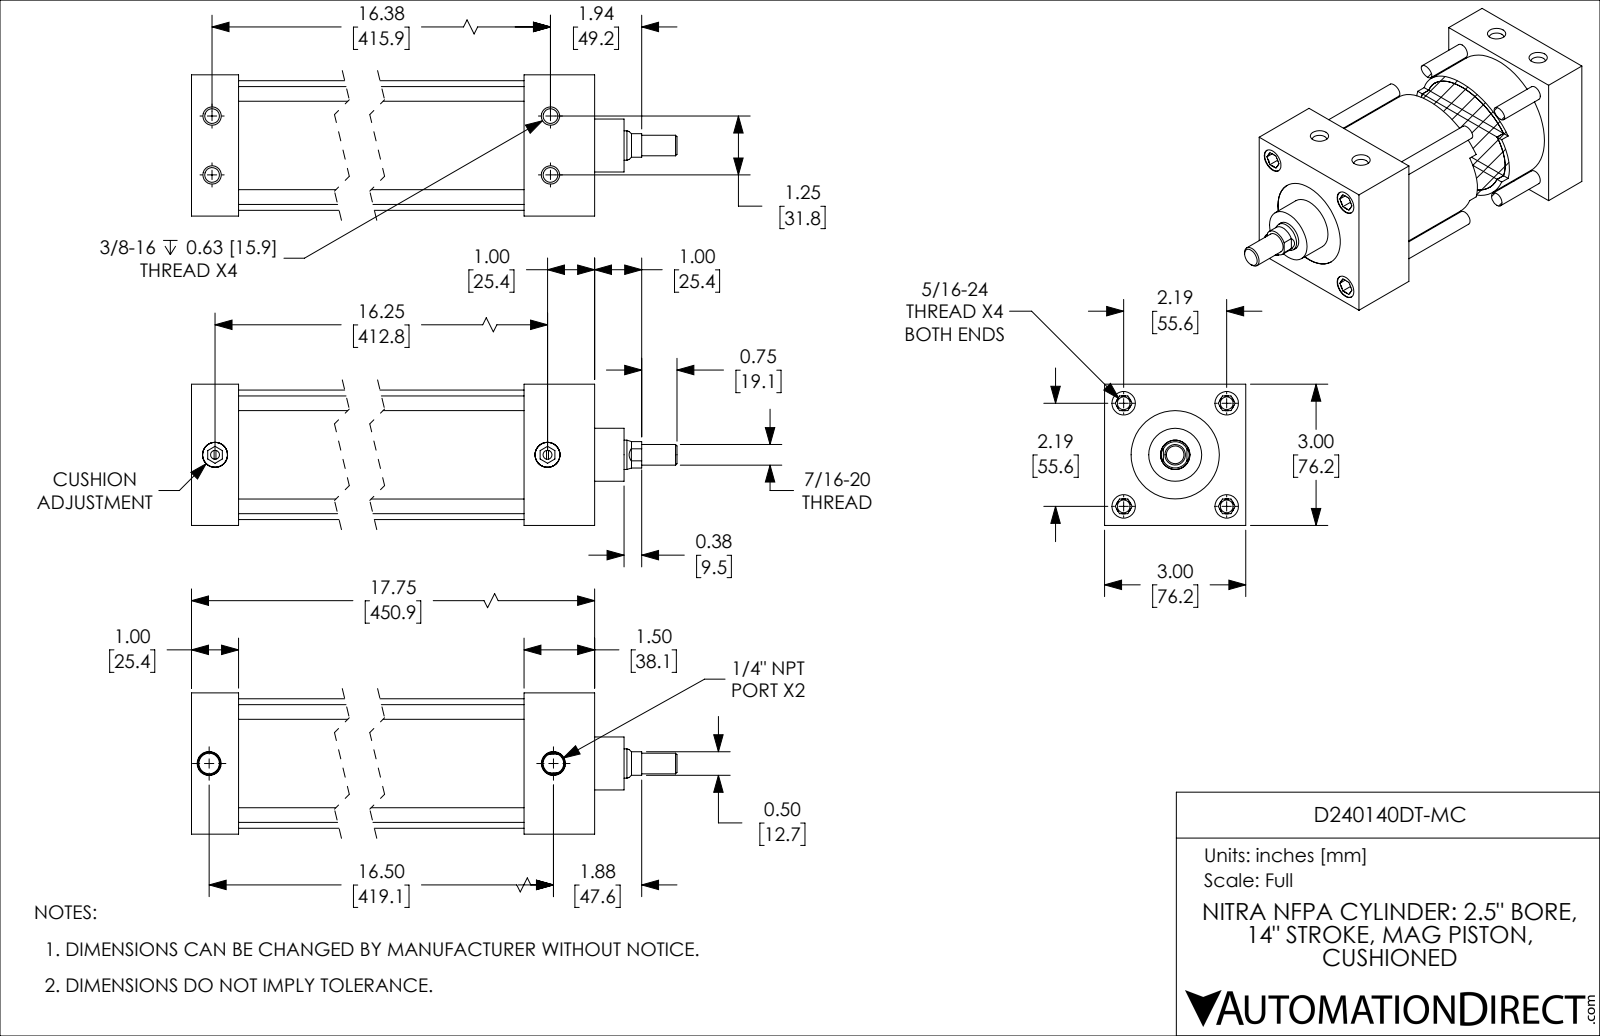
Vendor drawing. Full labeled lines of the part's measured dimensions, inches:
Part name (STEP PRODUCT): D240140DT-MC_CUSHION; D240140DT-MC_PISTON_KK1; D240140DT-MC; D240140DT-MC_BODY
STEP written by: SolidWorks 2019 (CONFIG_CONTROL_DESIGN)
Units: inches
Bodies: 4 solids, 248 faces (90 planar, 78 cylindrical, 80 other)
Overall size (bounding box): 19.5 × 3 × 3
Volume: 53 in³ · Surface area: 447.6 in²
Round holes (diameter × count): ⌀0.272 ×4, ⌀0.313 ×4, ⌀0.5 ×4, ⌀0.19 ×2, ⌀0.438 ×2, ⌀0.531 ×2, ⌀0.626 ×1, ⌀1.875 ×1, ⌀2.501 ×1
Round bosses / shafts (diameter × count): ⌀0.312 ×4, ⌀0.532 ×2, ⌀2.751 ×1, ⌀2.499 ×1, ⌀1.125 ×1, ⌀0.624 ×1, ⌀0.437 ×1
Partial cylindrical surfaces — rounded edges, fillets, slot ends (radius × count): R0.281 ×1
Main face-to-face distances: 3, 1, 16.25, 15.25, 17.75, 16.75, 1.5, 1.25, 2.25, 14
Hole centre spacings: 1.548, 2.19, 16.449, 0.628, 0.628, 1.25, 3.097, 16.375
